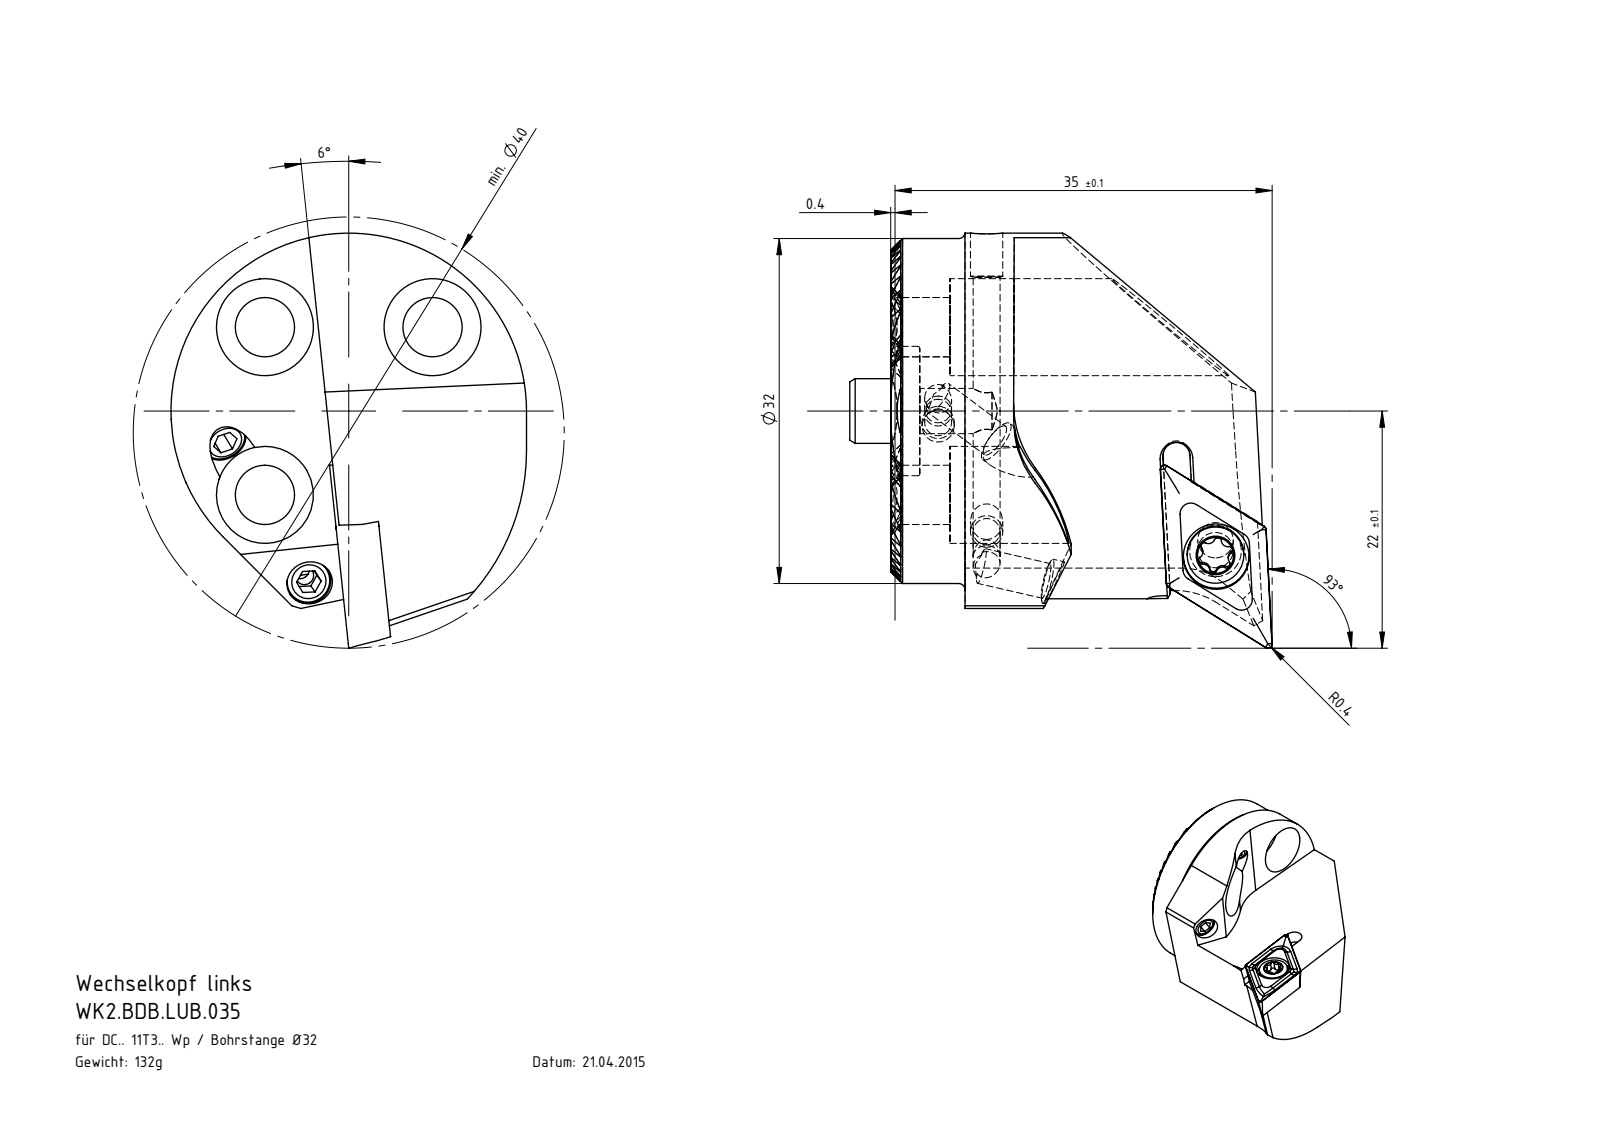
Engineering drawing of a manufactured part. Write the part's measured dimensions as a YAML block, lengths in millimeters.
part_name: "KVT_MB_600_030; WKX-ER1.004.005_A_PreviewCfg; DCMT11T304; WK2-ER1.001.012_A_Fertigbearbeitung (+3 more)"
step_written_by: "SolidWorks 2017 (AUTOMOTIVE_DESIGN)"
units: millimeters
bodies: {solids: 12, faces: 563, planar: 195, cylindrical: 190, other: 178}
overall_size: [39.2, 38.51, 33]
volume: 16499
surface_area: 8470
round_holes:
  - {diameter: 2.38, count: 3}
  - {diameter: 2.5, count: 3}
  - {diameter: 3.3, count: 3}
  - {diameter: 4.2, count: 3}
  - {diameter: 5.5, count: 3}
  - {diameter: 9, count: 3}
  - {diameter: 1.7, count: 2}
  - {diameter: 3, count: 1}
  - {diameter: 4.4, count: 1}
  - {diameter: 6.1, count: 1}
  - {diameter: 12, count: 1}
round_bosses_or_shafts:
  - {diameter: 4, count: 3}
  - {diameter: 3, count: 3}
  - {diameter: 32, count: 1}
  - {diameter: 6, count: 1}
  - {diameter: 5.25, count: 1}
partial_cylinders:
  - {radius: 0.12, count: 22}
  - {radius: 0.34, count: 6}
  - {radius: 0.59, count: 6}
  - {radius: 20, count: 2}
  - {radius: 1.25, count: 1}
  - {radius: 7, count: 1}
  - {radius: 10, count: 1}
  - {radius: 16.5, count: 1}
face_to_face_distances: [1.3, 2.6, 3.9, 5.2, 6.5, 12.99, 11.69, 14.29, 7.8, 10.39]
hole_center_spacings: [11, 15.56, 22.01]
